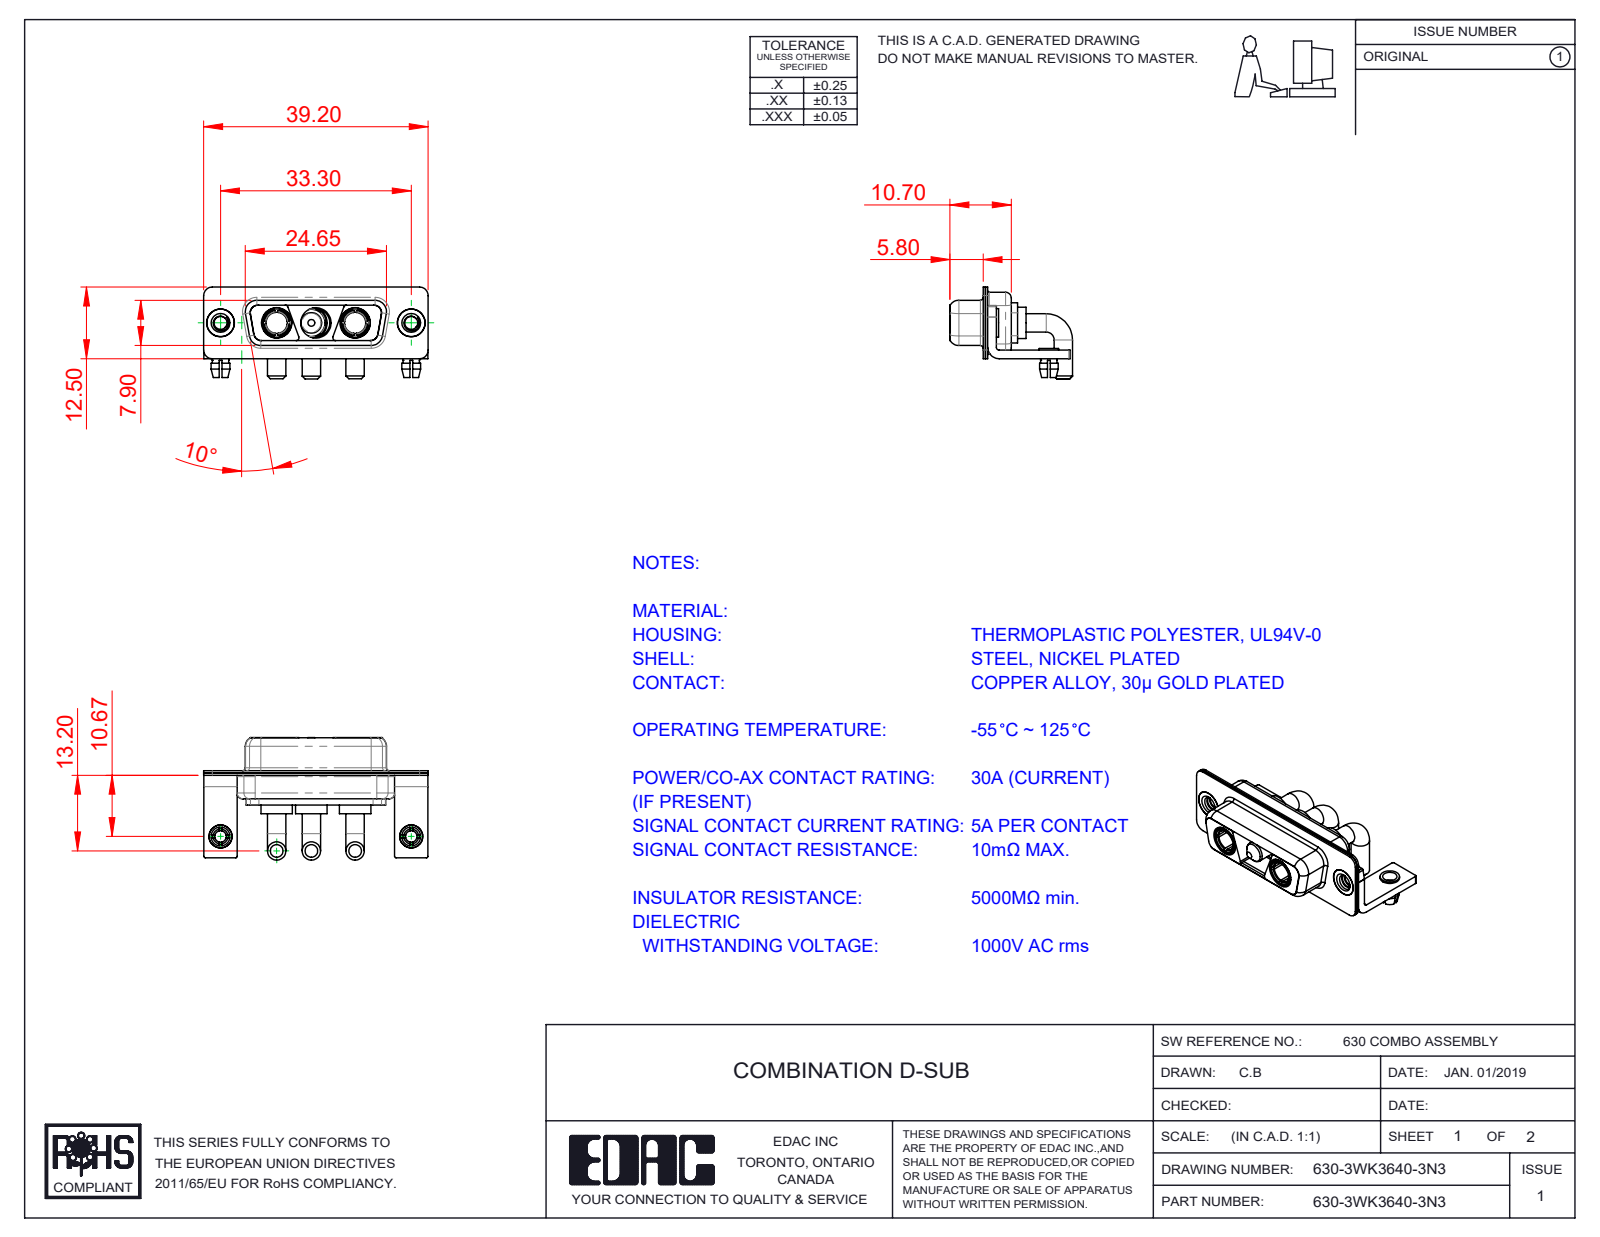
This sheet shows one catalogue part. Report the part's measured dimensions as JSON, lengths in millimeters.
{"part_name": "630Combo Shell Front_15 Contacts; 630-3WK3640-3N3; 630Combo Shell Rear_15 Contacts; 630Combo Threaded Rivet_3 (+5 more)", "step_written_by": "SolidWorks 2020 (CONFIG_CONTROL_DESIGN)", "units": "millimeters", "bodies": {"solids": 15, "faces": 620, "planar": 208, "cylindrical": 263, "other": 149}, "overall_size": [39.2, 21.4, 16.05], "volume_mm3": 2882, "surface_area_mm2": 6544, "round_holes": [[4.85, 5], [5.3, 3], [2, 2], [2.26, 2], [2.5, 2], [3.2, 2], [3.7, 2], [4, 2], [4.05, 2]], "round_bosses_or_shafts": [[3.2, 6], [5.5, 3], [5.2, 3], [4.75, 3], [3.75, 3], [5, 2], [4.96, 2], [4.95, 2]], "partial_cylinders_radius": [[0.25, 16], [1.5, 16], [2, 13], [1.35, 12], [0.5, 9], [1.6, 8], [0.6, 4], [0.65, 4]], "face_to_face_distances": [0.4, 0.8, 1.4, 1.5, 0.45, 8.45, 1.8, 8.9, 7.05, 2.3], "hole_center_spacings": [6.85, 9.8, 16.65, 23.5, 33.3, 13.7]}
